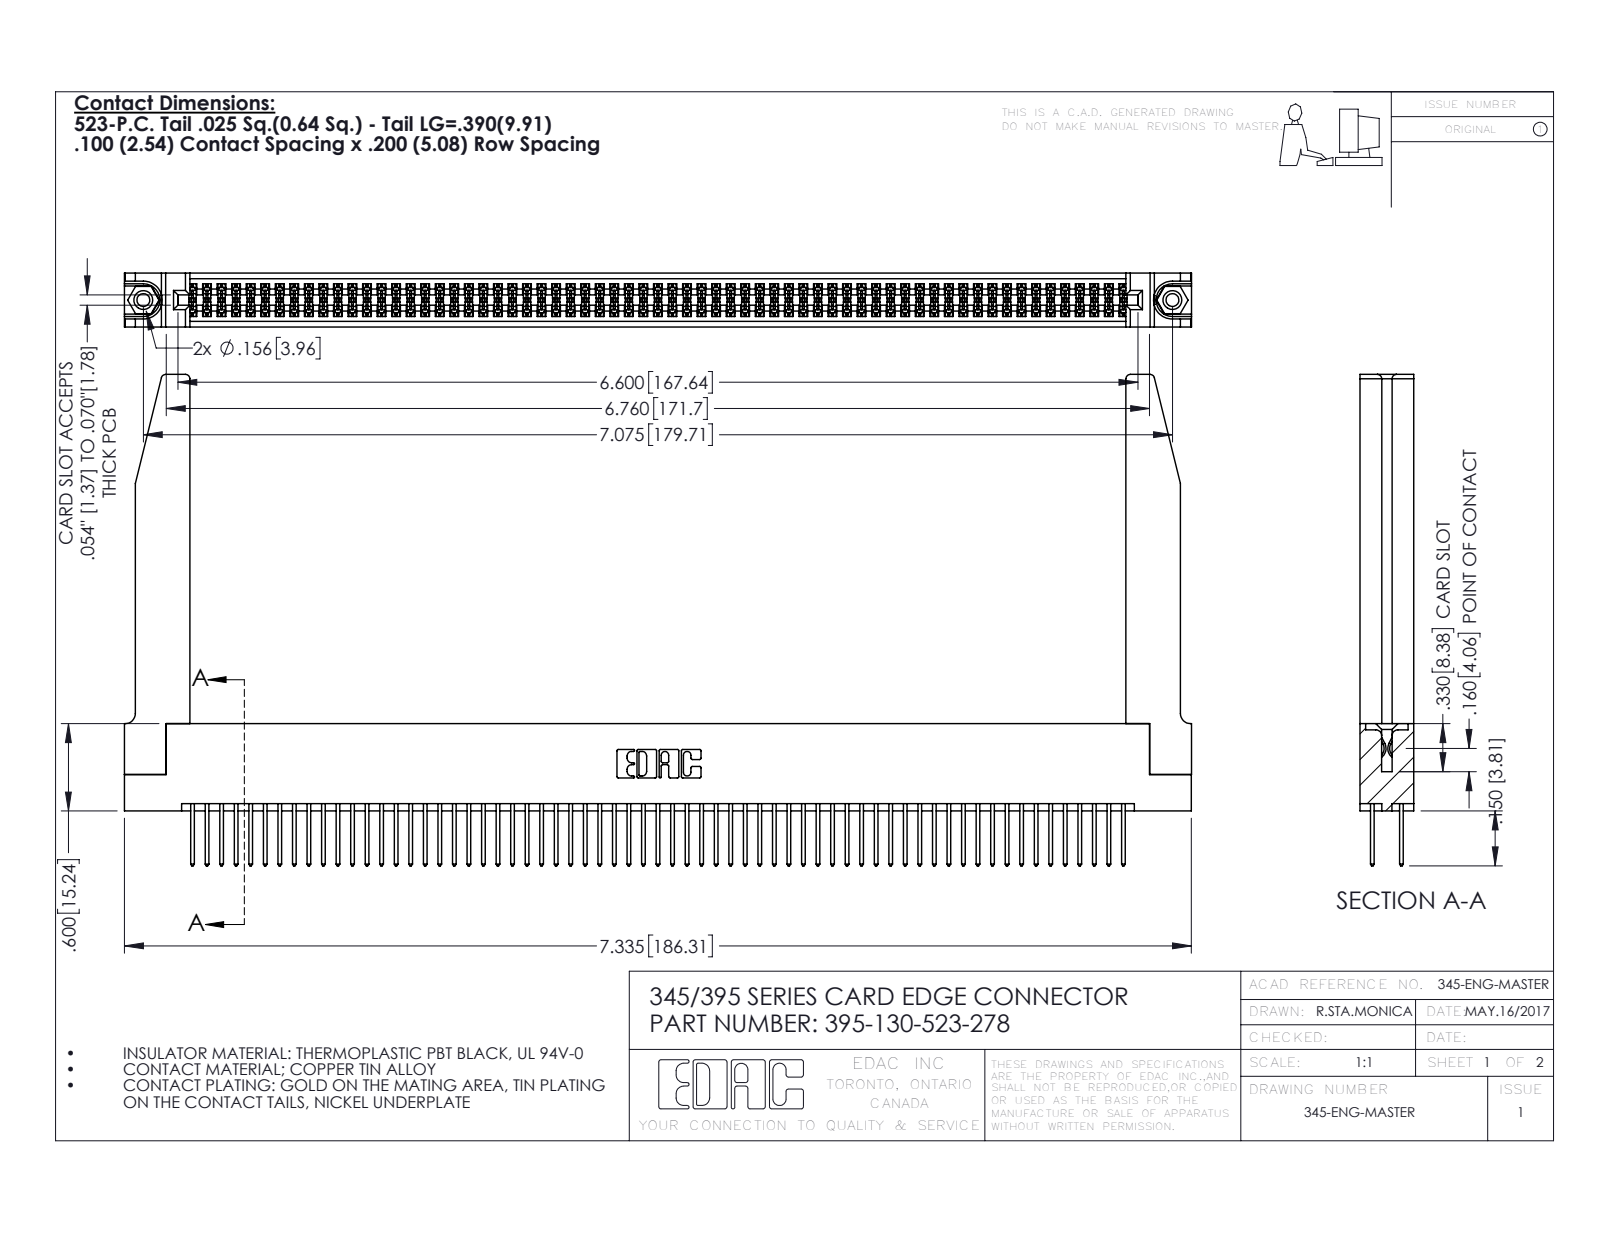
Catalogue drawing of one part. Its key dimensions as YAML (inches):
part_name: "395-130-523-278; 345-220-078_345-220-078; 345 Part_Flush Mounting Lugs - 0.156 Dia-TH; 345-250-001_345-250-001-102 (+1 more)"
step_written_by: "SolidWorks 2016 (CONFIG_CONTROL_DESIGN)"
units: inches
bodies: {solids: 135, faces: 6860, planar: 4512, cylindrical: 2296, other: 52}
overall_size: [7.336, 3.377, 0.37]
volume: 1.608
surface_area: 55.71
round_holes:
  - {diameter: 0.089, count: 2}
  - {diameter: 0.125, count: 2}
  - {diameter: 0.156, count: 2}
  - {diameter: 0.064, count: 1}
round_bosses_or_shafts:
  - {diameter: 0.155, count: 2}
partial_cylinders:
  - {radius: 0.006, count: 195}
  - {radius: 0.01, count: 130}
  - {radius: 0.01, count: 22}
  - {radius: 0.03, count: 8}
  - {radius: 0.007, count: 6}
  - {radius: 0.031, count: 6}
  - {radius: 0.026, count: 3}
  - {radius: 0.014, count: 2}
face_to_face_distances: [0.072, 0.298, 0.37, 0.2, 0.098, 0.272, 0.025, 0.225, 0.175, 0.148]
hole_center_spacings: [0.27, 6.839, 7.075]
